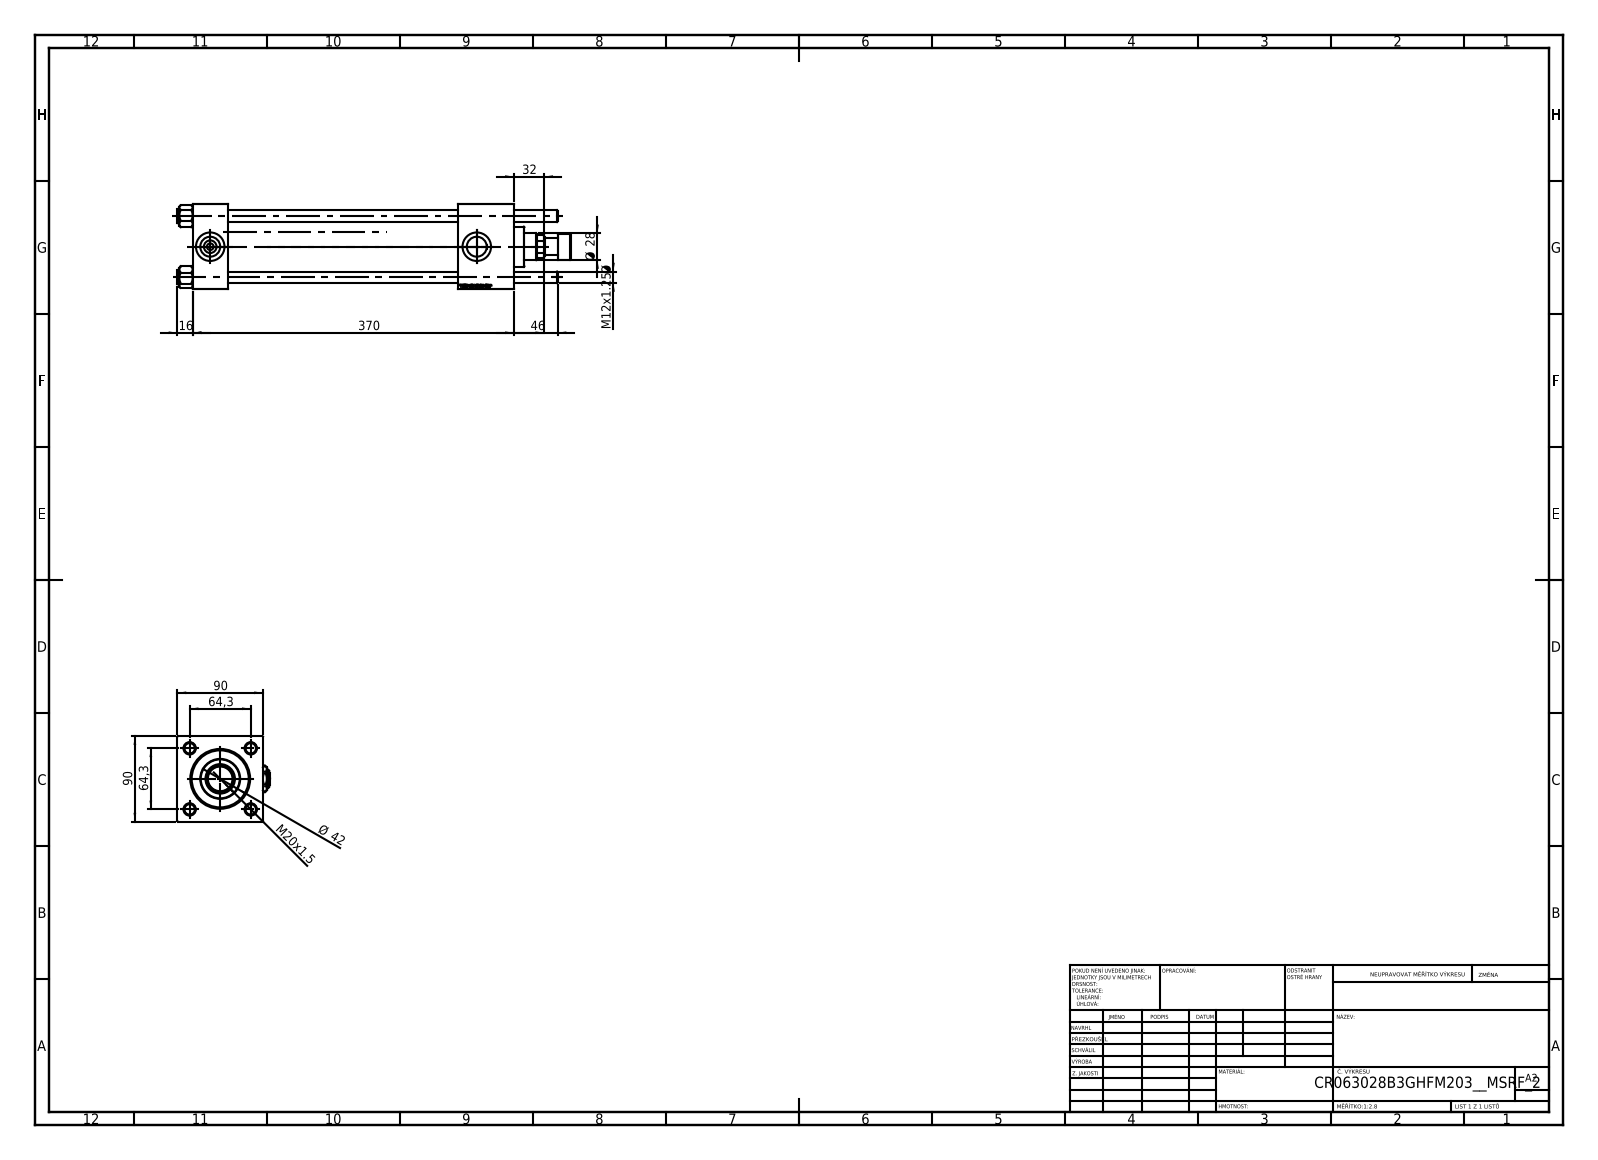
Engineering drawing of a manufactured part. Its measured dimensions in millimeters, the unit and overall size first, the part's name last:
Units: millimetres
Overall size (bounding box): 414 × 97 × 90
Round holes (diameter × count): ⌀12 ×4, ⌀7 ×2, ⌀20.96 ×2, ⌀30 ×2, ⌀18.5 ×1, ⌀28 ×1, ⌀31 ×1, ⌀50 ×1, ⌀60 ×1, ⌀63 ×1
Round bosses / shafts (diameter × count): ⌀15 ×4, ⌀69 ×1, ⌀42 ×1, ⌀27 ×1, ⌀18 ×1
Main face-to-face distances: 90, 37, 301, 338, 59, 279, 242, 309.3, 272.3, 30.3
Hole centre spacings: 45.47, 64.3, 90.93, 280.5
Volume: 1 296 000 mm³ · Surface area: 322 637 mm²
Bodies: 14 solids, 1271 faces (483 planar, 92 cylindrical, 696 other)
Part name (STEP PRODUCT): V215_VC_A; Zatka_pro_OIL_PORT; V215CR_B-1; V215CR_ROD_END_F (+3 more)
STEP written by: SolidWorks 2019 (CONFIG_CONTROL_DESIGN)
